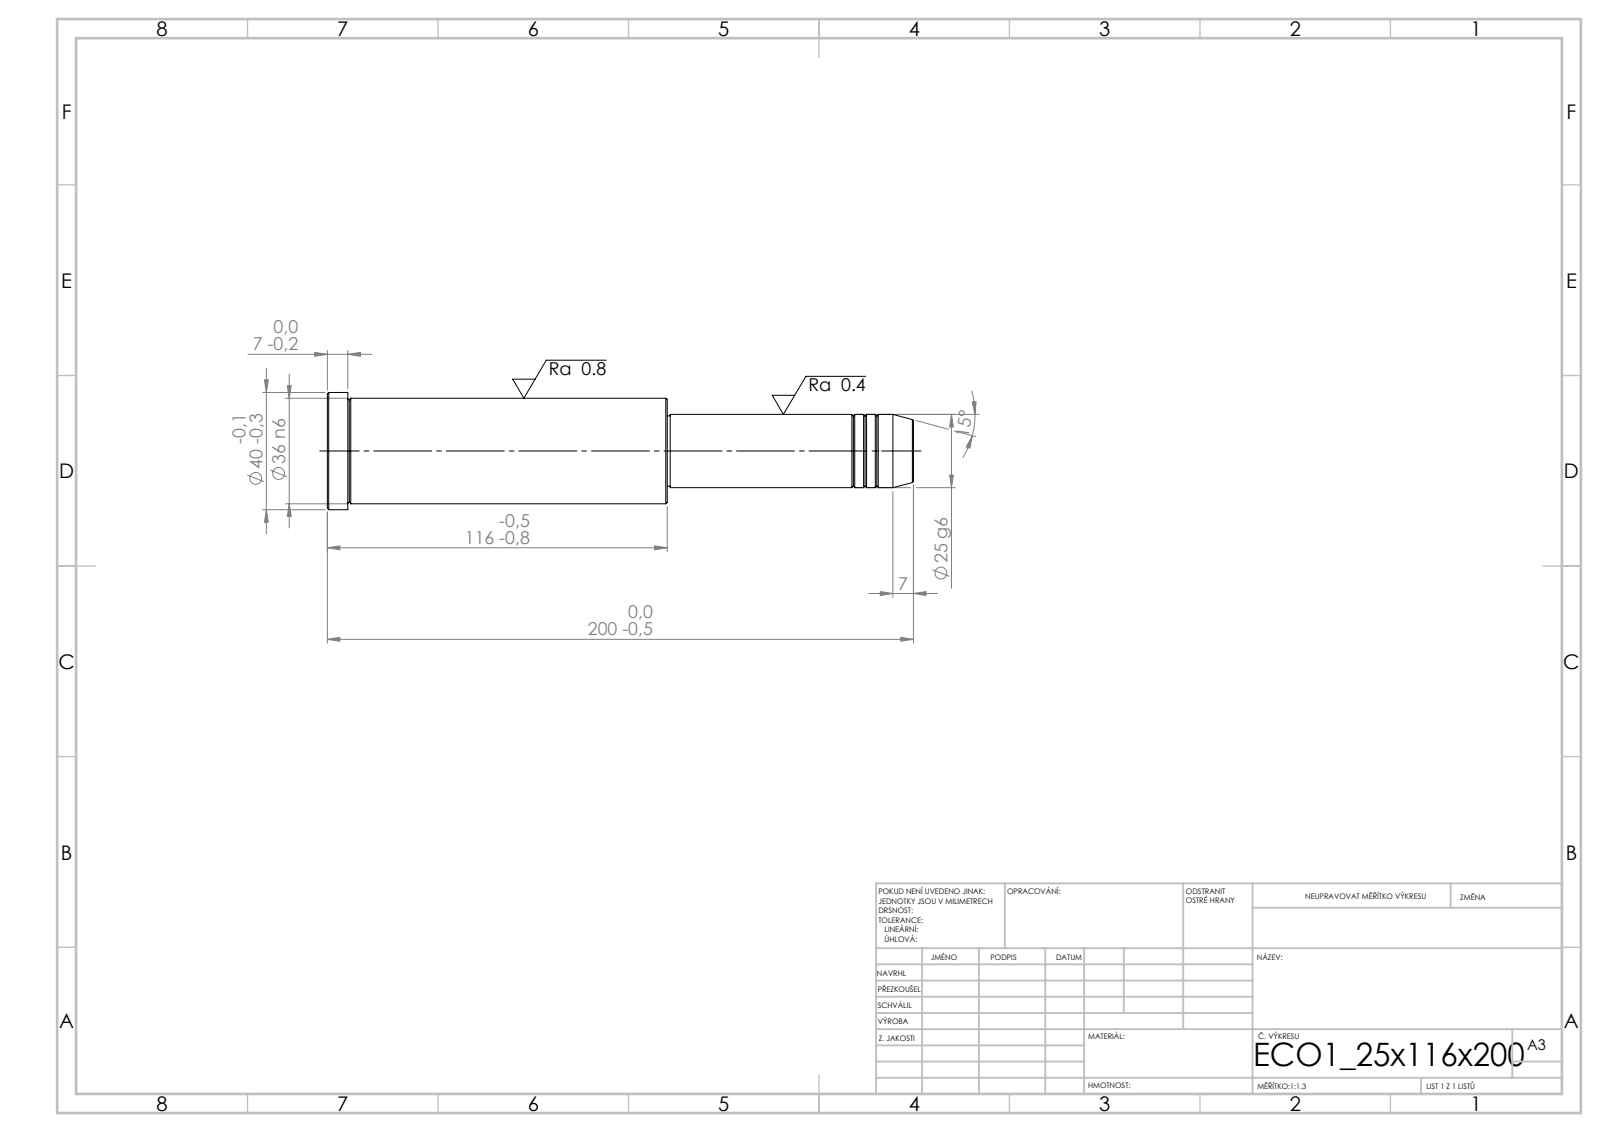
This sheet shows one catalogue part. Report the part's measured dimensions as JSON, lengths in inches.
{"step_written_by": "SolidWorks 2019 (CONFIG_CONTROL_DESIGN)", "units": "inches", "bodies": {"solids": 1, "faces": 43, "planar": 5, "cylindrical": 14, "other": 24}, "overall_size": [7.874, 1.575, 1.575], "volume_in3": 9.781, "surface_area_in2": 34.63, "round_bosses_or_shafts": [[1.575, 1], [1.417, 1], [0.984, 1], [0.945, 1]], "face_to_face_distances": [4.567, 3.307, 7.874, 7.598, 4.291, 0.276, 3.268, 0.039, 4.331, 4.606]}
